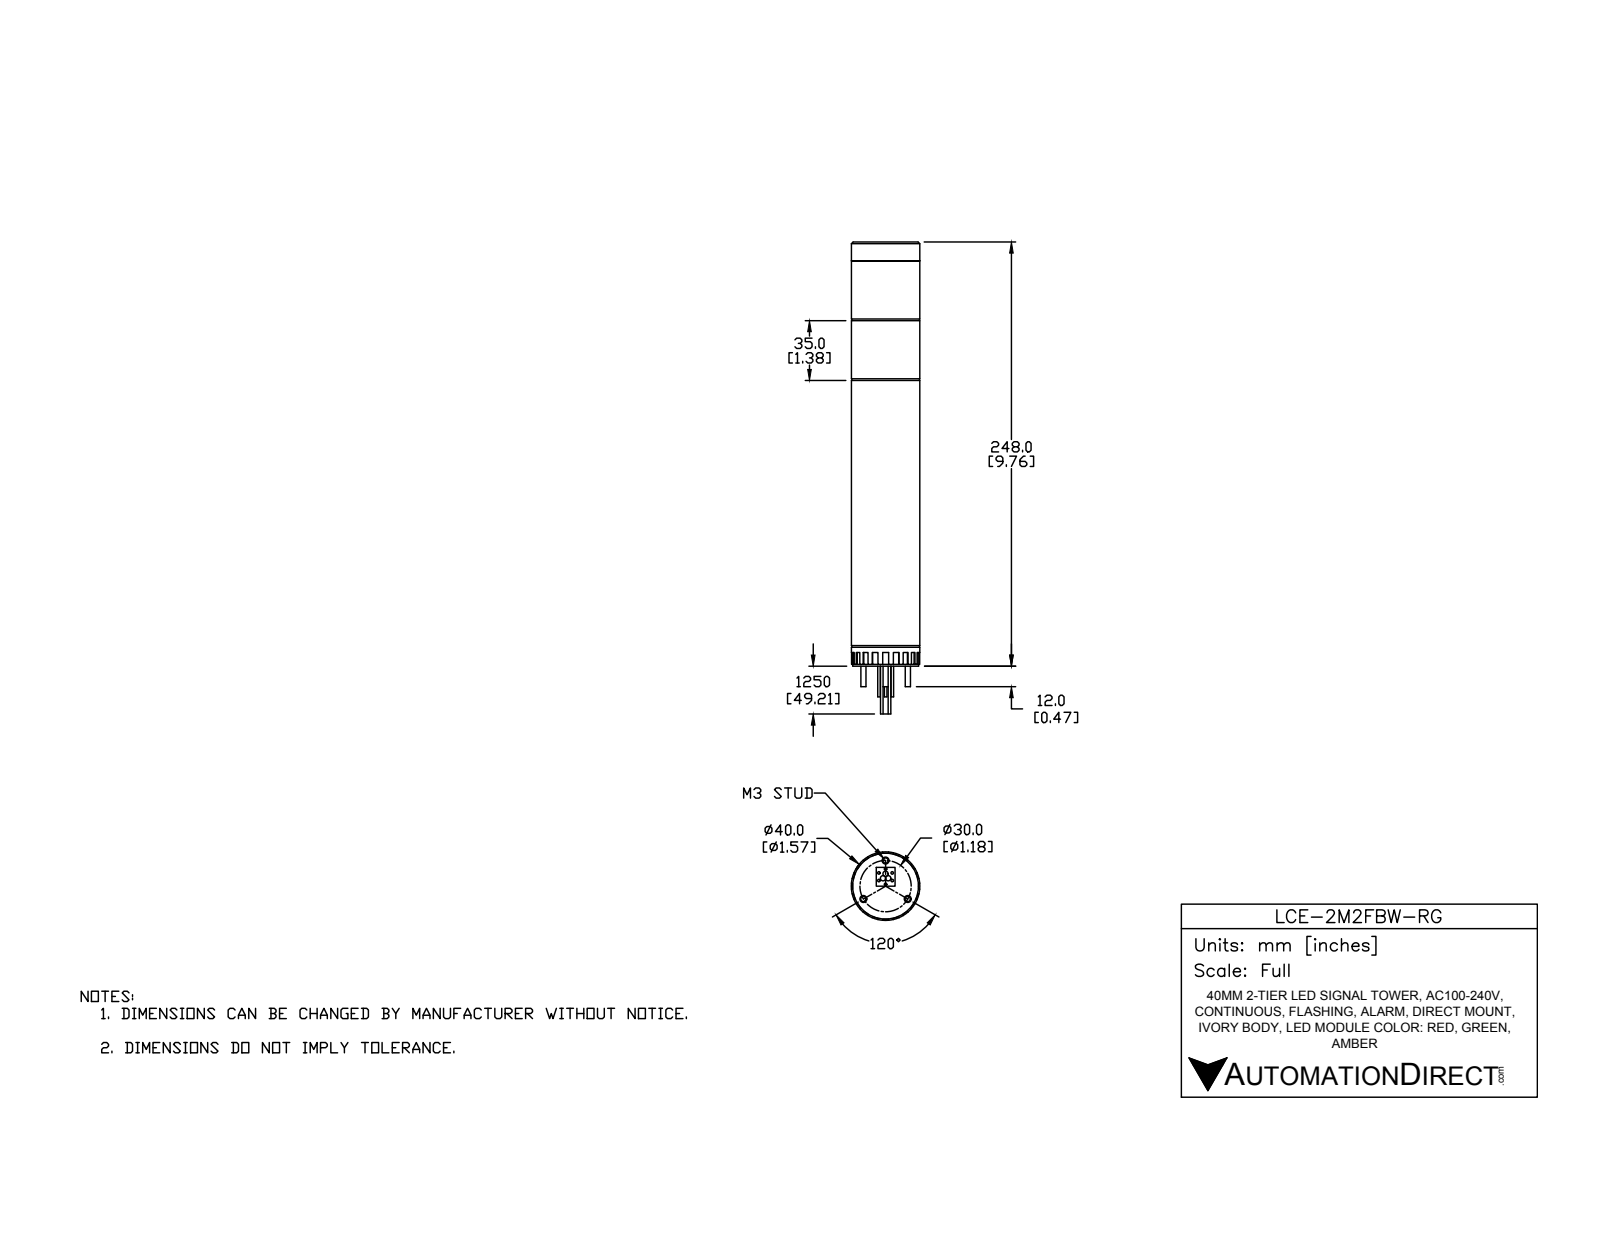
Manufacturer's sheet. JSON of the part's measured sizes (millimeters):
{"part_name": "LCE-2M2FBW-RG", "step_written_by": "SolidWorks 2016 (AUTOMOTIVE_DESIGN)", "units": "millimeters", "bodies": {"solids": 26, "faces": 222, "planar": 158, "cylindrical": 60, "other": 4}, "overall_size": [276, 40, 40], "volume_mm3": 310854, "surface_area_mm2": 56249, "round_holes": [[4, 3], [8, 1]], "round_bosses_or_shafts": [[1.5, 10], [3, 3], [2.5, 3], [40, 1], [39.5, 1], [38.5, 1], [5.5, 1]], "face_to_face_distances": [1, 35, 34, 156, 191, 11, 236, 167, 202, 36], "hole_center_spacings": [15, 25.98]}
